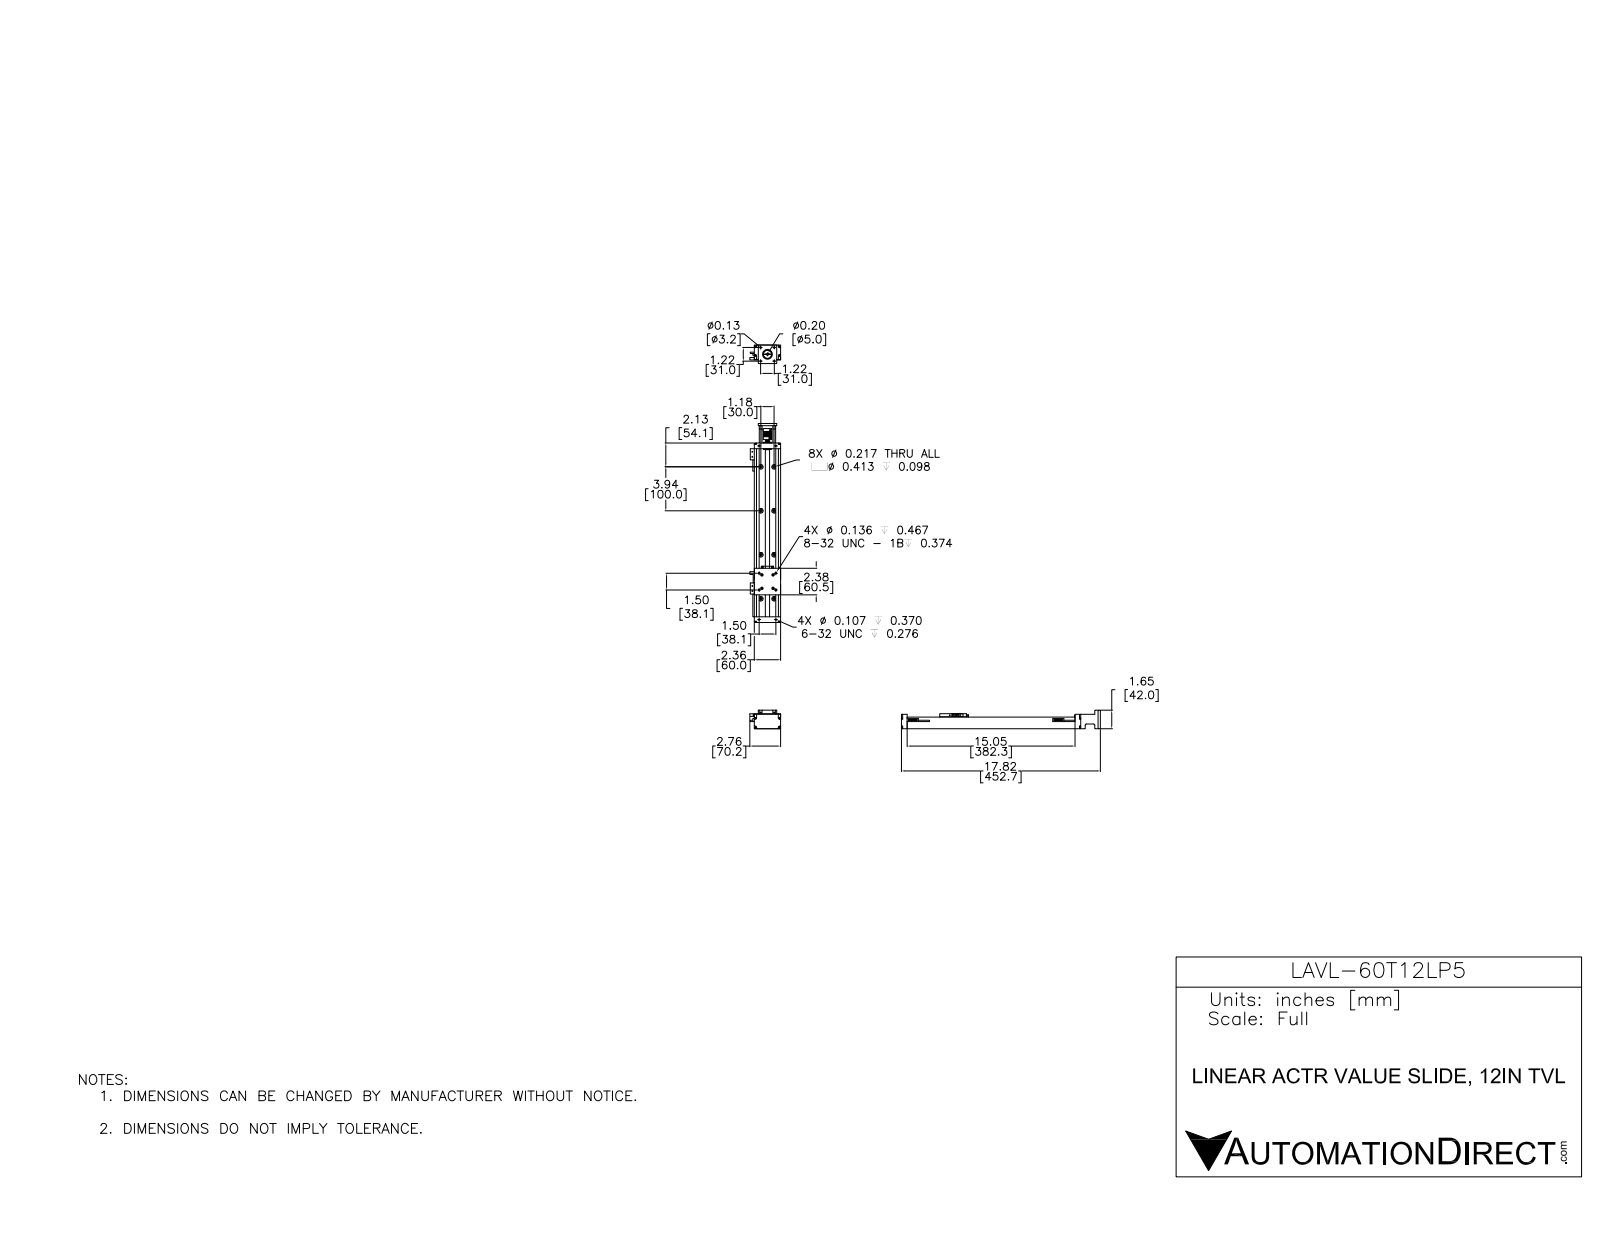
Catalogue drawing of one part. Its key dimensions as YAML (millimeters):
part_name: "LAVL-60T12LP5; LAVL-60T06LP5-CAR; LAVL-60T12LP5-RAIL"
step_written_by: "SolidWorks 2015 (AUTOMOTIVE_DESIGN)"
units: millimeters
bodies: {solids: 19, faces: 887, planar: 332, cylindrical: 384, other: 171}
overall_size: [452.7, 70.2, 42]
volume: 399400
surface_area: 188700
round_holes:
  - {diameter: 3.3, count: 12}
  - {diameter: 2.7, count: 10}
  - {diameter: 5.5, count: 8}
  - {diameter: 10.5, count: 8}
  - {diameter: 2.3, count: 6}
  - {diameter: 3.5, count: 6}
  - {diameter: 2.2, count: 4}
  - {diameter: 3, count: 4}
  - {diameter: 3.2, count: 4}
  - {diameter: 3.2, count: 4}
  - {diameter: 3.8, count: 4}
  - {diameter: 5.6, count: 4}
round_bosses_or_shafts:
  - {diameter: 5.6, count: 4}
  - {diameter: 5.3, count: 4}
  - {diameter: 4, count: 2}
  - {diameter: 19, count: 1}
  - {diameter: 17.5, count: 1}
  - {diameter: 17.1, count: 1}
  - {diameter: 15.9, count: 1}
  - {diameter: 12.9, count: 1}
partial_cylinders:
  - {radius: 2.8, count: 8}
  - {radius: 1.2, count: 4}
  - {radius: 5.4, count: 4}
  - {radius: 6.8, count: 4}
  - {radius: 1.2, count: 3}
  - {radius: 4.8, count: 3}
  - {radius: 1.4, count: 2}
  - {radius: 1.6, count: 2}
face_to_face_distances: [5.1, 54.9, 60, 49.8, 11.3, 16.4, 26.5, 21.4, 10.1, 13]
hole_center_spacings: [54.9, 27.7, 58.8, 31, 32.7, 38.1, 12.2, 12.9]
